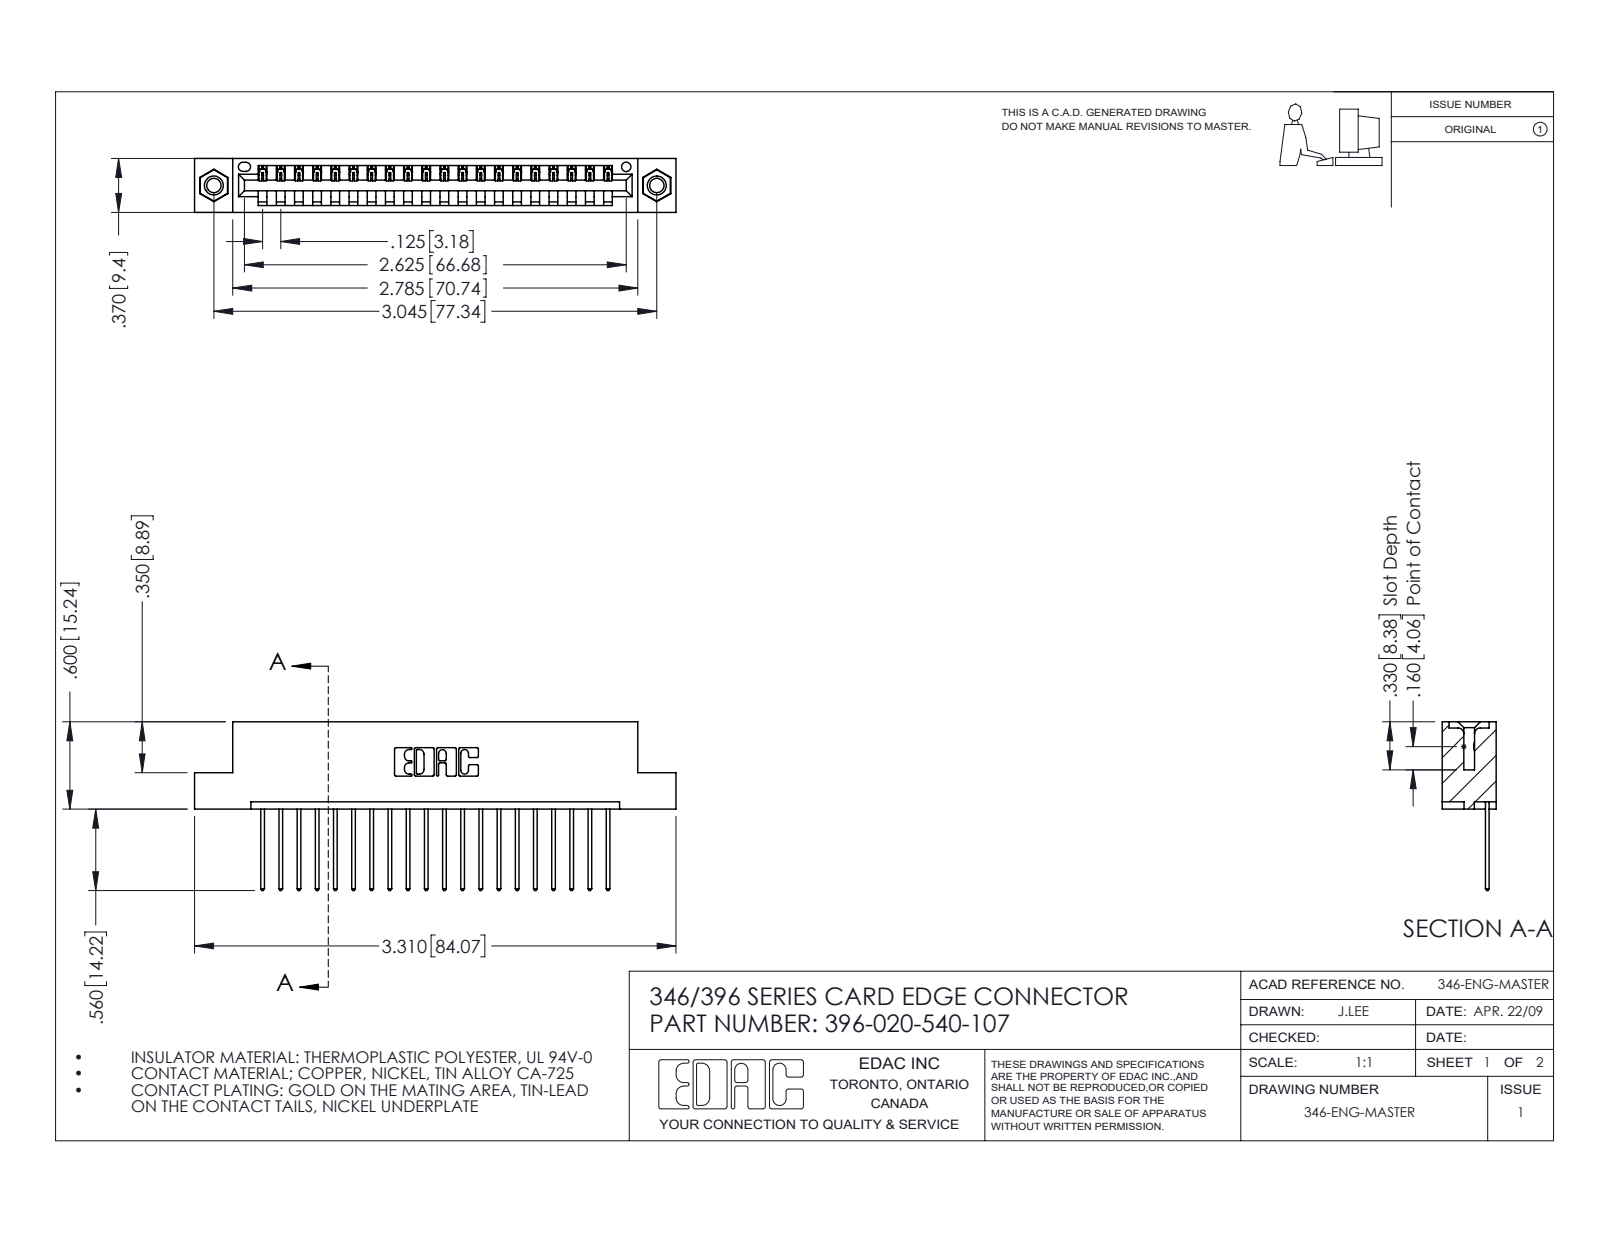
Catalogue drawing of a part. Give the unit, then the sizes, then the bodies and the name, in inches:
Units: inches
Overall size (bounding box): 3.31 × 1.16 × 0.37
Round holes (diameter × count): ⌀0.098 ×2, ⌀0.125 ×2, ⌀0.156 ×2, ⌀0.064 ×1
Round bosses / shafts (diameter × count): ⌀0.155 ×2
Partial cylindrical surfaces — rounded edges, fillets, slot ends (radius × count): R0.006 ×40, R0.01 ×40, R0.01 ×22, R0.007 ×6, R0.031 ×6, R0.026 ×3, R0.031 ×2, R0.04 ×2
Main face-to-face distances: 0.048, 0.322, 0.25, 0.37, 0.072, 0.298, 0.025, 0.148, 0.222, 0.1
Hole centre spacings: 0.246, 2.837, 3.045
Volume: 0.483 in³ · Surface area: 15.32 in²
Bodies: 23 solids, 1342 faces (908 planar, 418 cylindrical, 16 other)
Part name (STEP PRODUCT): 396-020-540-107; 345-250-001_345-250-005-103; 346 Part_Flush Mounting Lugs - 0.156 Dia-TI; 345-292-001_345-293-140
STEP written by: SolidWorks 2016 (CONFIG_CONTROL_DESIGN)
